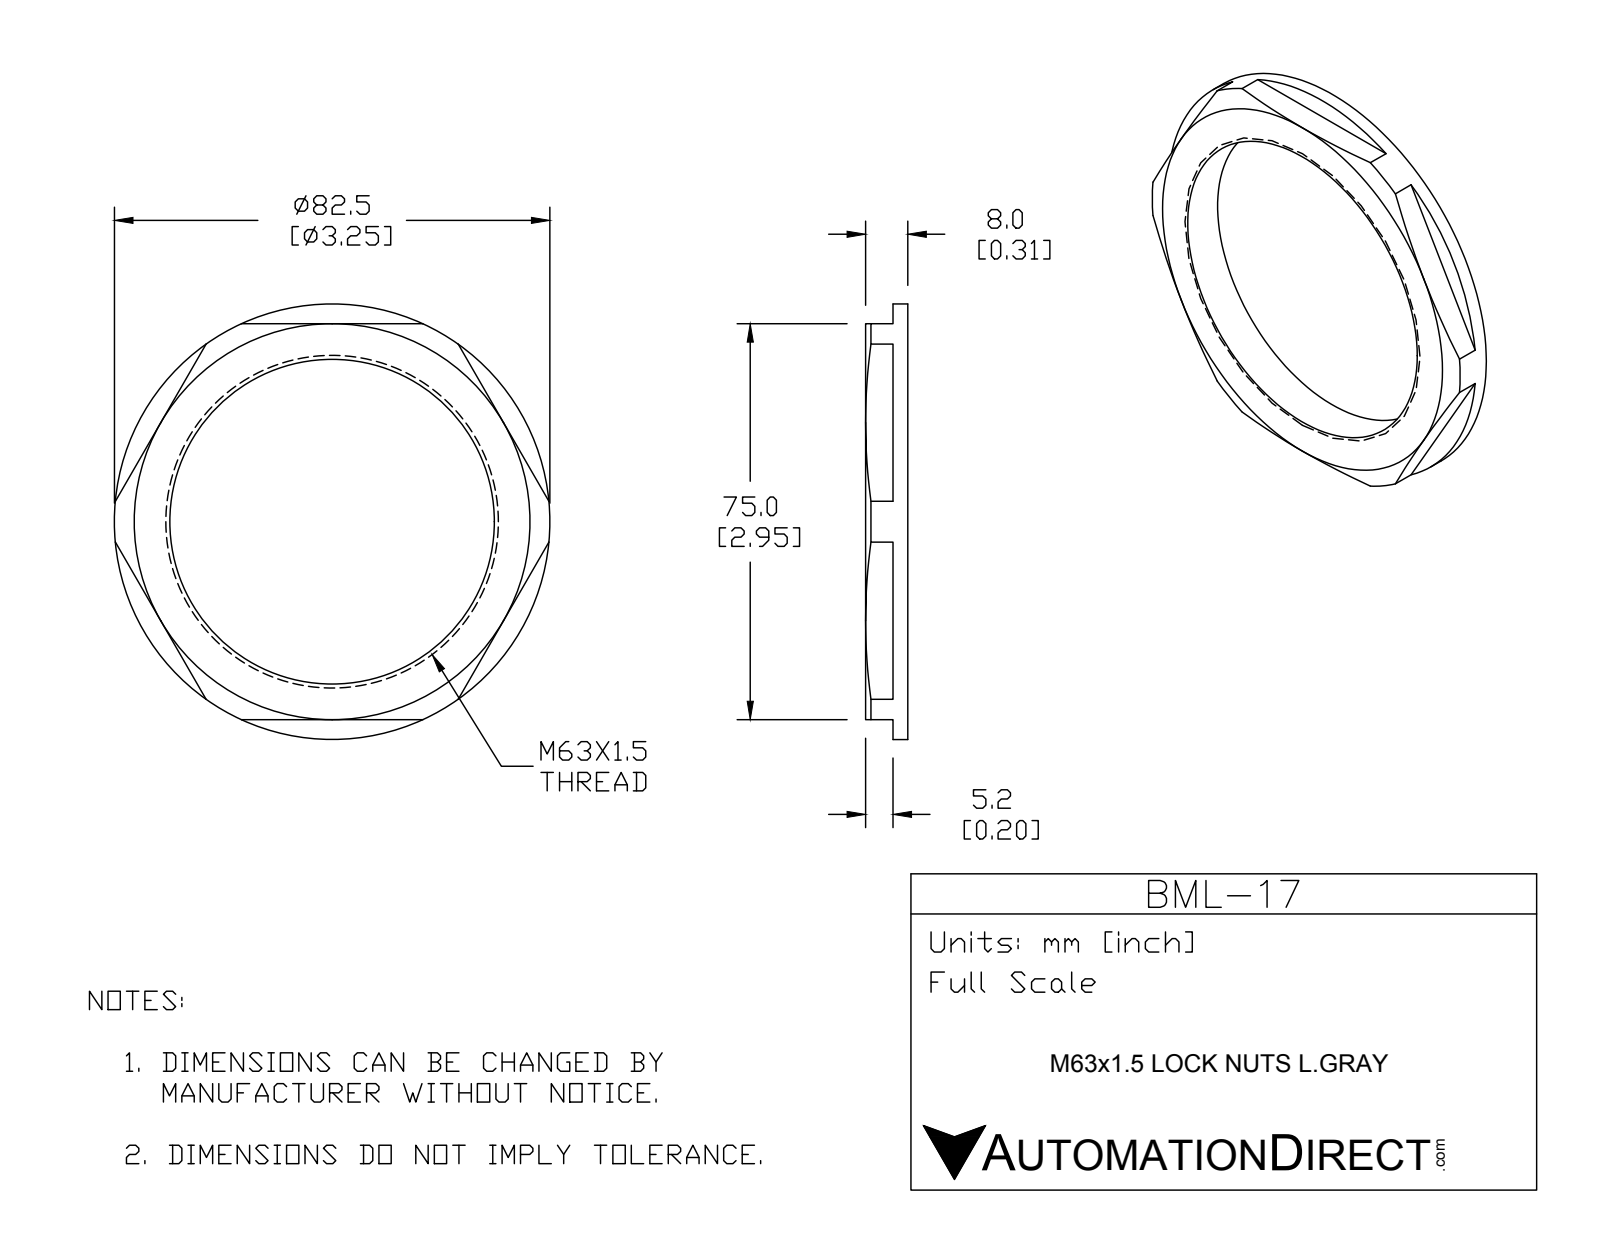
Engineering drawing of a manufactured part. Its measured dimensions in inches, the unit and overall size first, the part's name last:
Units: inches
Overall size (bounding box): 3.248 × 3.248 × 0.315
Round holes (diameter × count): ⌀0.059 ×3, ⌀2.421 ×1
Round bosses / shafts (diameter × count): ⌀3.248 ×1
Main face-to-face distances: 0.315, 0.11, 0.205, 2.953, 0.098, 0.303
Hole centre spacings: 1.567, 2.714
Volume: 0.985 in³ · Surface area: 12.77 in²
Bodies: 1 solid, 33 faces (17 planar, 10 cylindrical, 6 other)
Part name (STEP PRODUCT): BML-17
STEP written by: SolidWorks 2015 (CONFIG_CONTROL_DESIGN)
